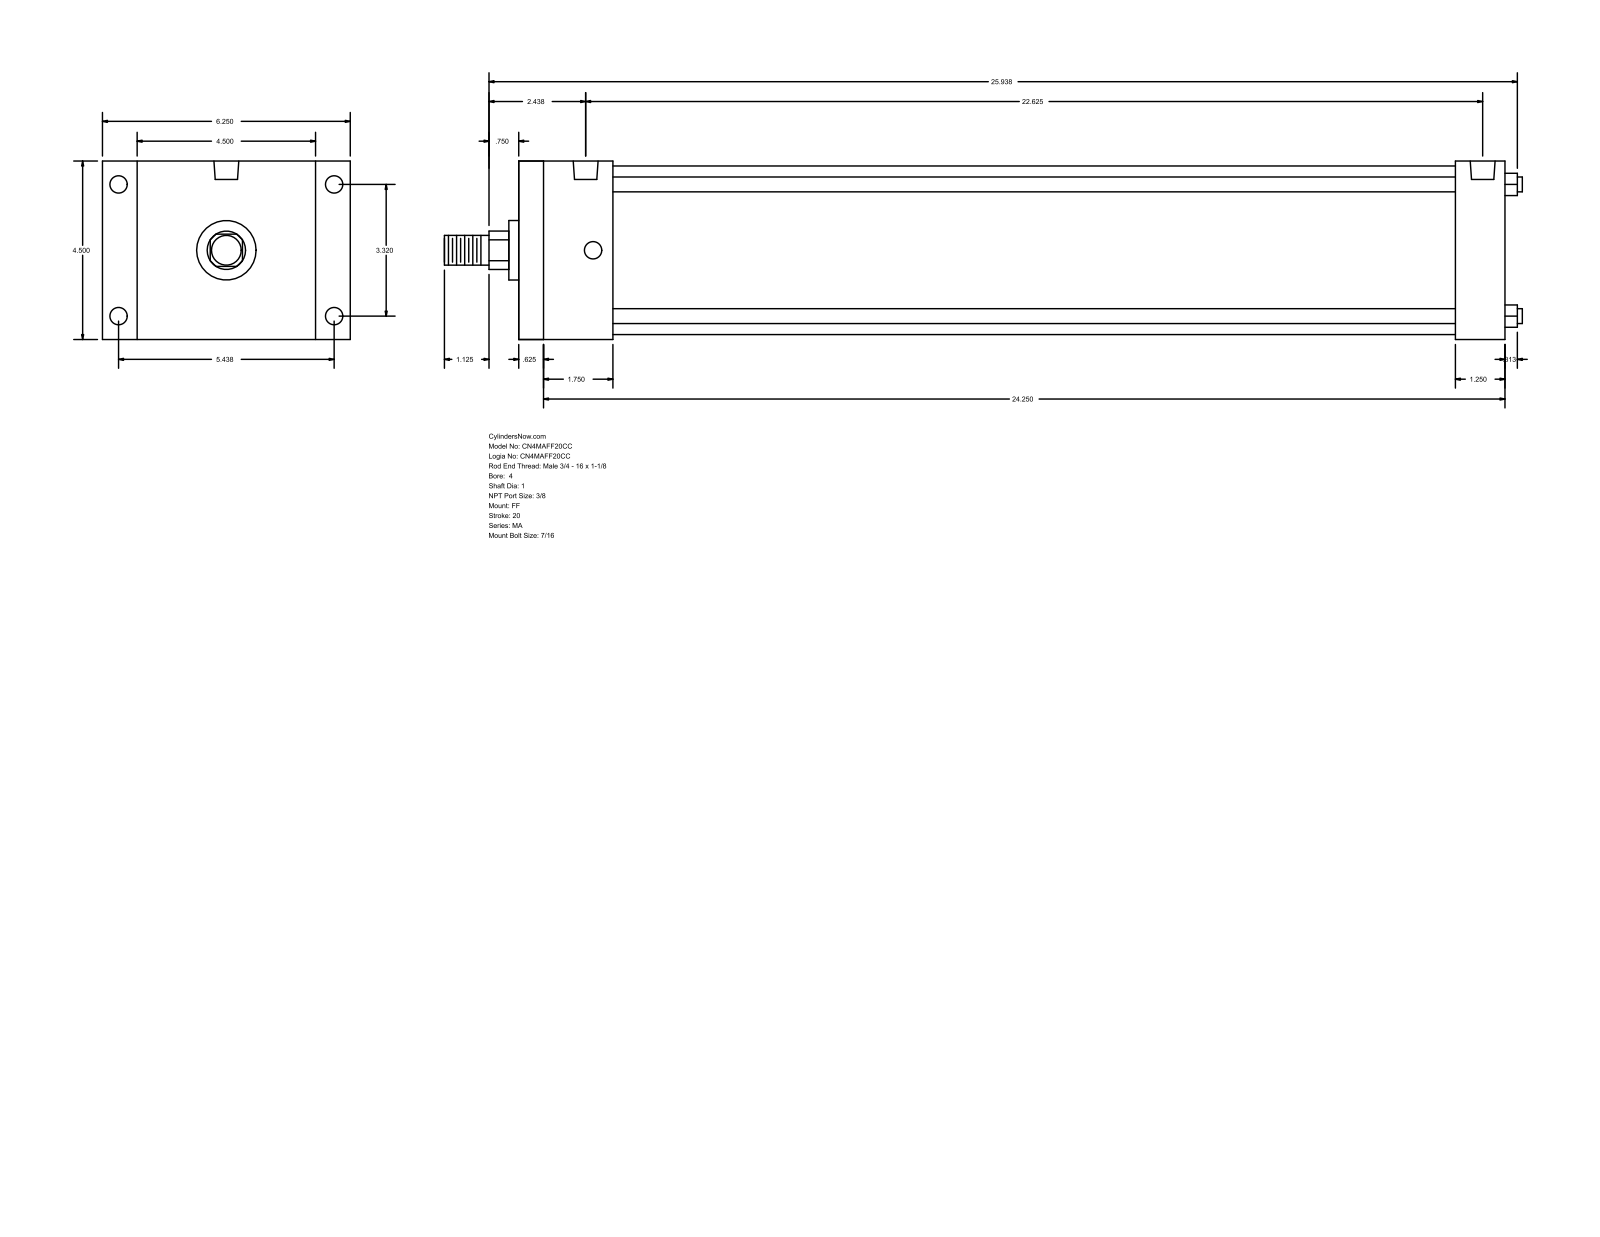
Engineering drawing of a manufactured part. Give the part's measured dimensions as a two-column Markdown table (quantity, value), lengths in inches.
| quantity | value |
| --- | --- |
| part name | MA_FF__0400_1 |
| STEP written by | GSSL Pune (CONFIG_CONTROL_DESIGN) |
| units | inches |
| bodies | 0 solids, 92 faces (64 planar, 28 cylindrical, 0 other) |
| overall size | 27.187 × 6.25 × 4.5 |
| round holes (diameter × count) | 0.437 × 8, 0.627 × 2 |
| round bosses / shafts (diameter × count) | 0.375 × 4, 4.25 × 1, 1.5 × 1, 1 × 1, 0.75 × 1 |
| partial cylindrical surfaces (radius × count) | 0.484 × 1 |
| main face-to-face distances | 4.5, 24.875, 0.625, 24.25, 0.875, 5.375, 23.625, 23, 1.25, 2.375 |
| hole center spacings | 0.187, 3.32, 5.438, 6.371, 22.25, 22.438, 22.625 |
